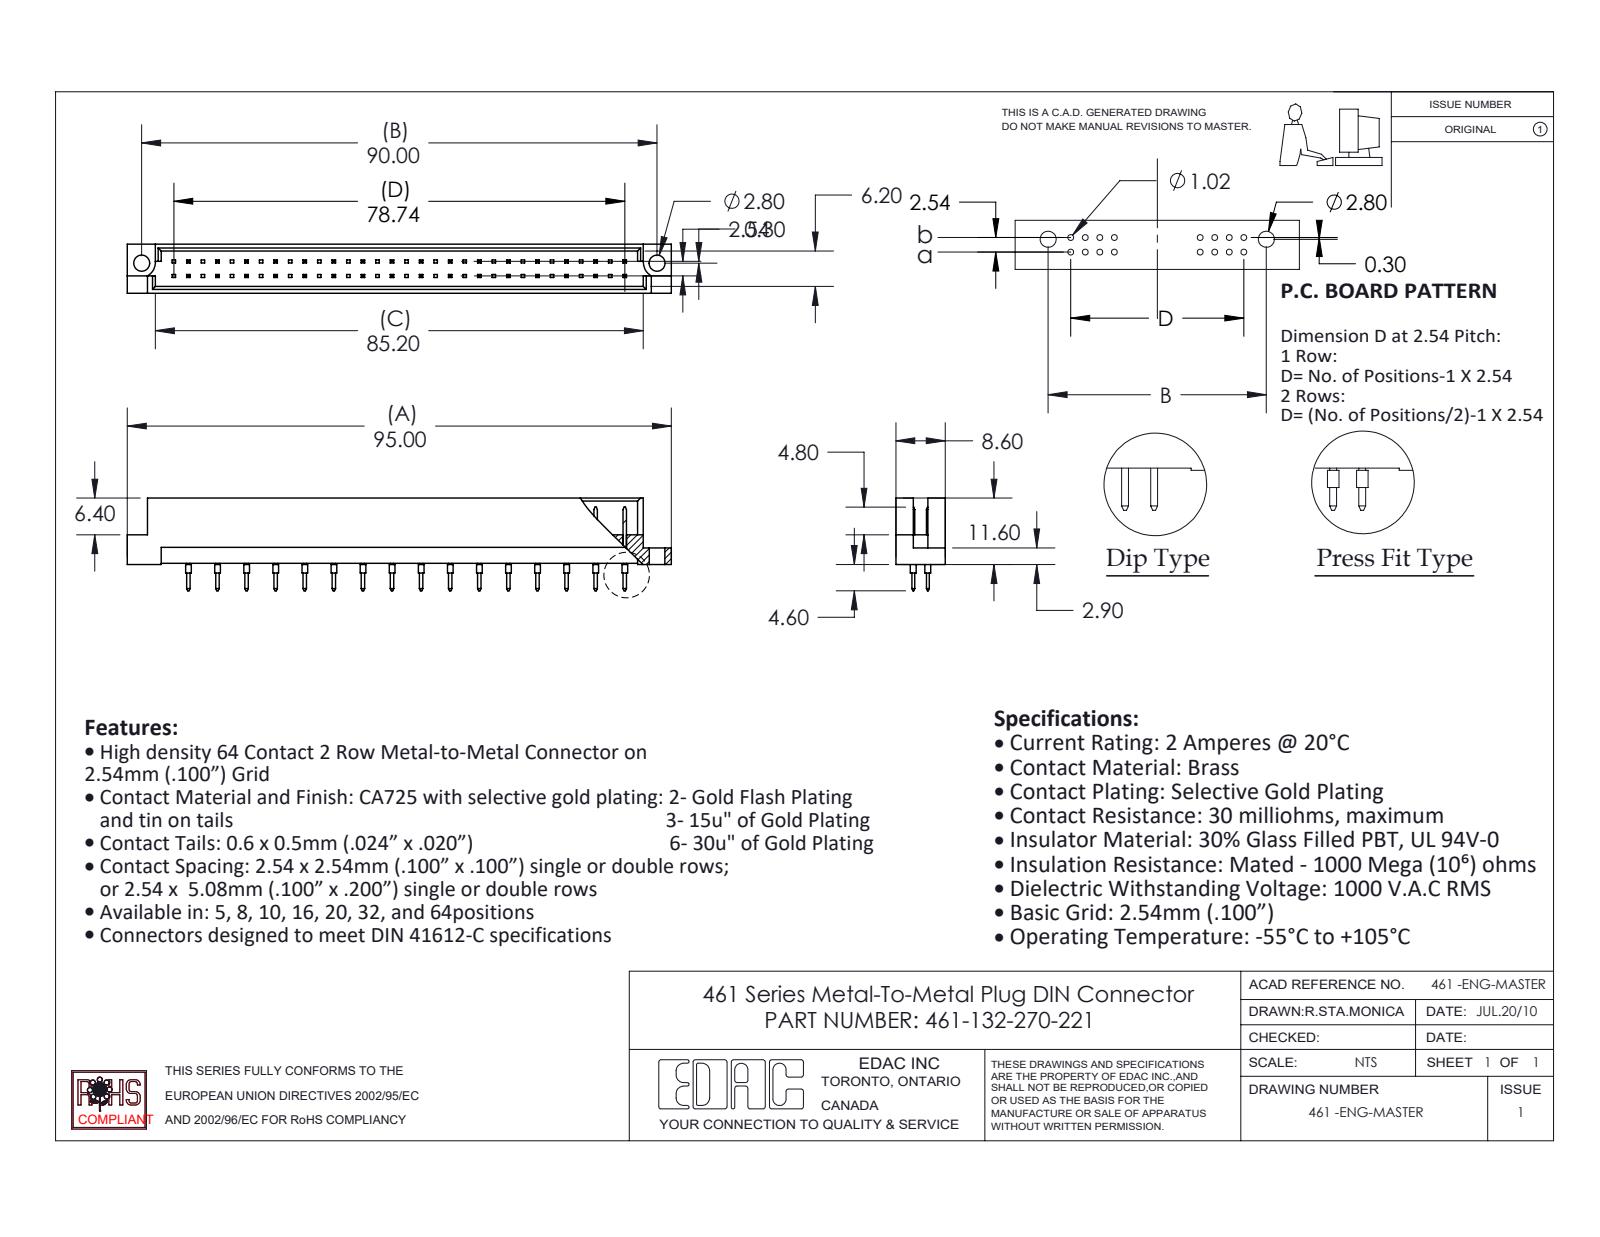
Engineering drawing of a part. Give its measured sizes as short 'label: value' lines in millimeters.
name: 461 Part_64; 461-132-270-221; 461-290_70
written by: SolidWorks 2020 (CONFIG_CONTROL_DESIGN)
unit: mm
bodies: 33 solids, 1009 faces (938 planar, 71 cylindrical, 0 other)
size: 95 × 16.2 × 8.6
volume: 4 816 mm³; area: 6 763 mm²
holes: 2× ⌀2.8
bosses: 32× ⌀1
rounds: 2× R2.8
face distances: 1.2, 7.4, 8.6, 6.2, 5, 2.54, 1.58, 3.28, 5.32, 2.08
hole spacings: 90
